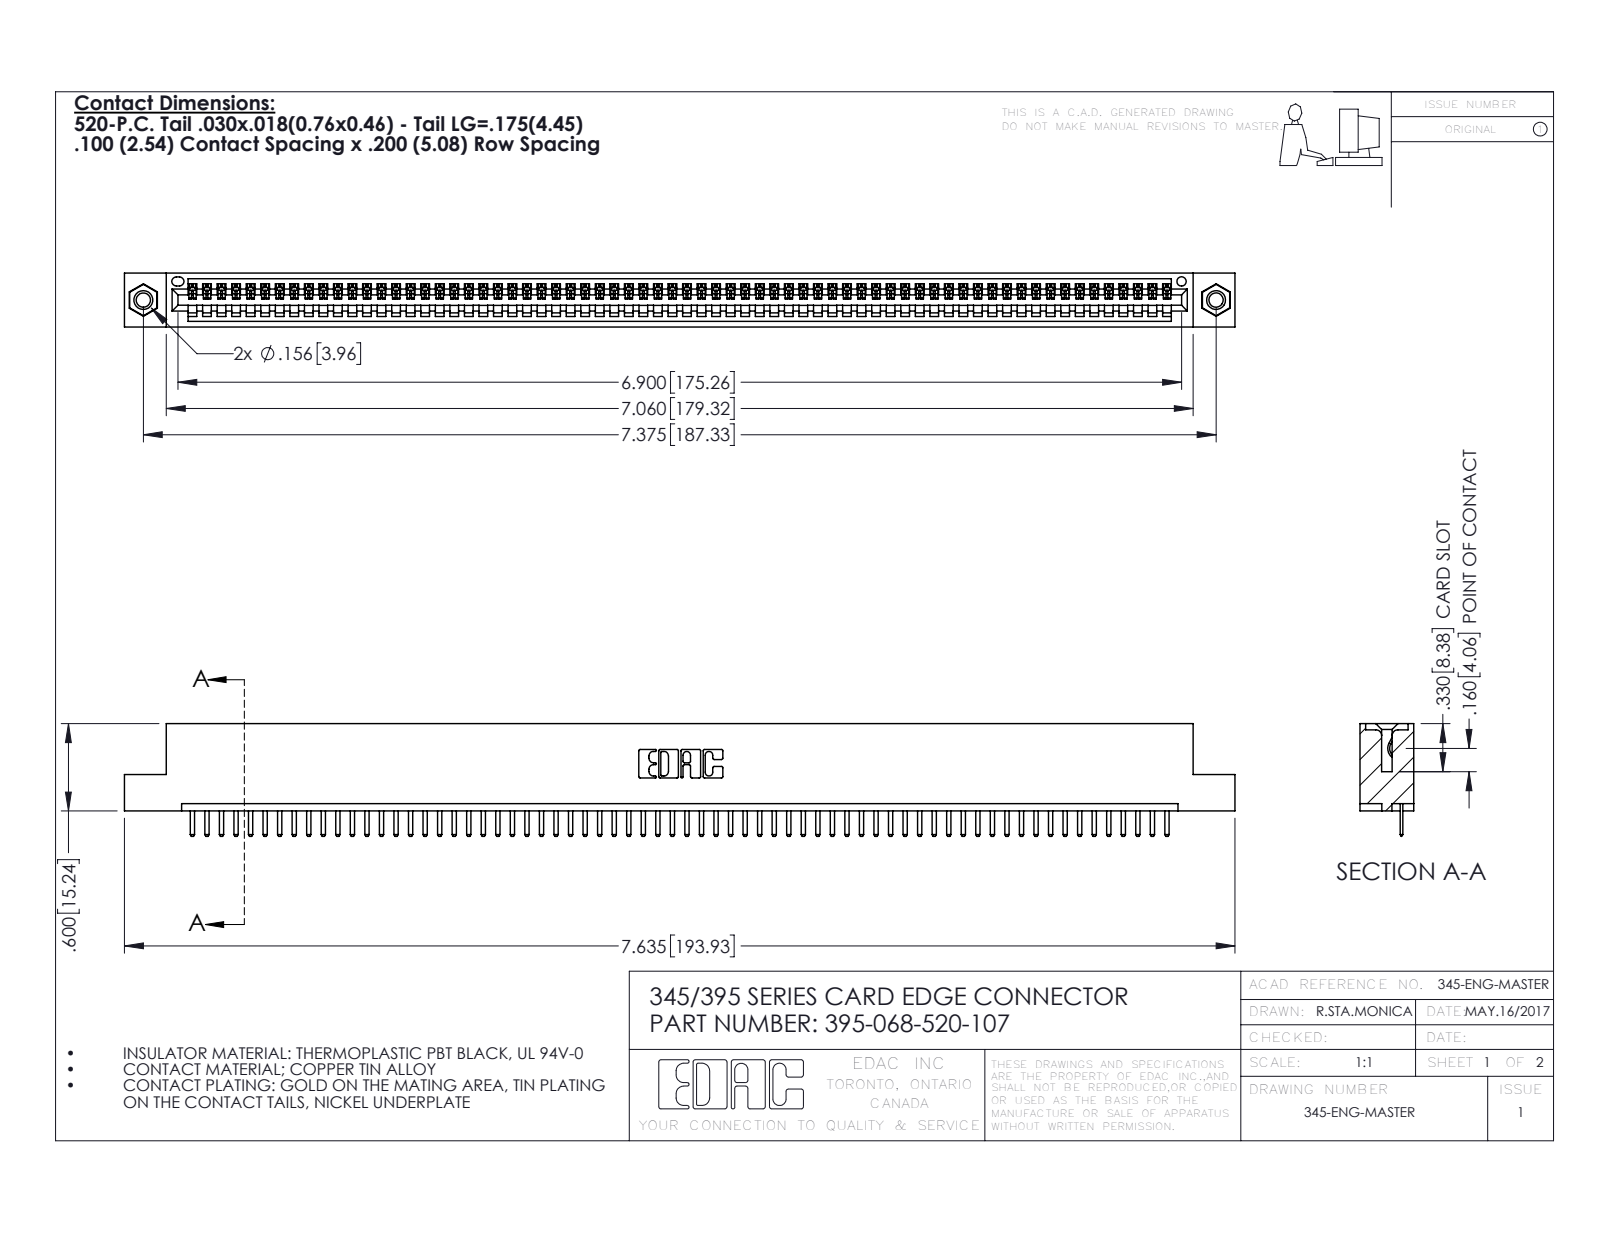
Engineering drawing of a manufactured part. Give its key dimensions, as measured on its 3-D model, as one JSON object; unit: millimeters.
{"part_name": "345-292-001_345-293-120; 345-250-001_345-250-005-103; 345 Part_Flush Mounting Lugs - 0.156 Dia-TI; 395-068-520-107", "step_written_by": "SolidWorks 2016 (CONFIG_CONTROL_DESIGN)", "units": "millimeters", "bodies": {"solids": 71, "faces": 4402, "planar": 2968, "cylindrical": 1418, "other": 16}, "overall_size": [193.9, 19.7, 9.4], "volume_mm3": 18420, "surface_area_mm2": 24230, "round_holes": [[2.5, 2], [3.2, 2], [4, 2], [1.6, 1]], "round_bosses_or_shafts": [[3.9, 2]], "partial_cylinders_radius": [[0.3, 138], [0.2, 136], [0.3, 22], [0.2, 6], [0.8, 6], [0.7, 3], [0.8, 2], [1, 2]], "face_to_face_distances": [1.8, 7.6, 9.4, 5.1, 2.5, 6.9, 0.6, 5.7, 1.8, 3.8], "hole_center_spacings": [6.9, 181.3, 187.3]}
